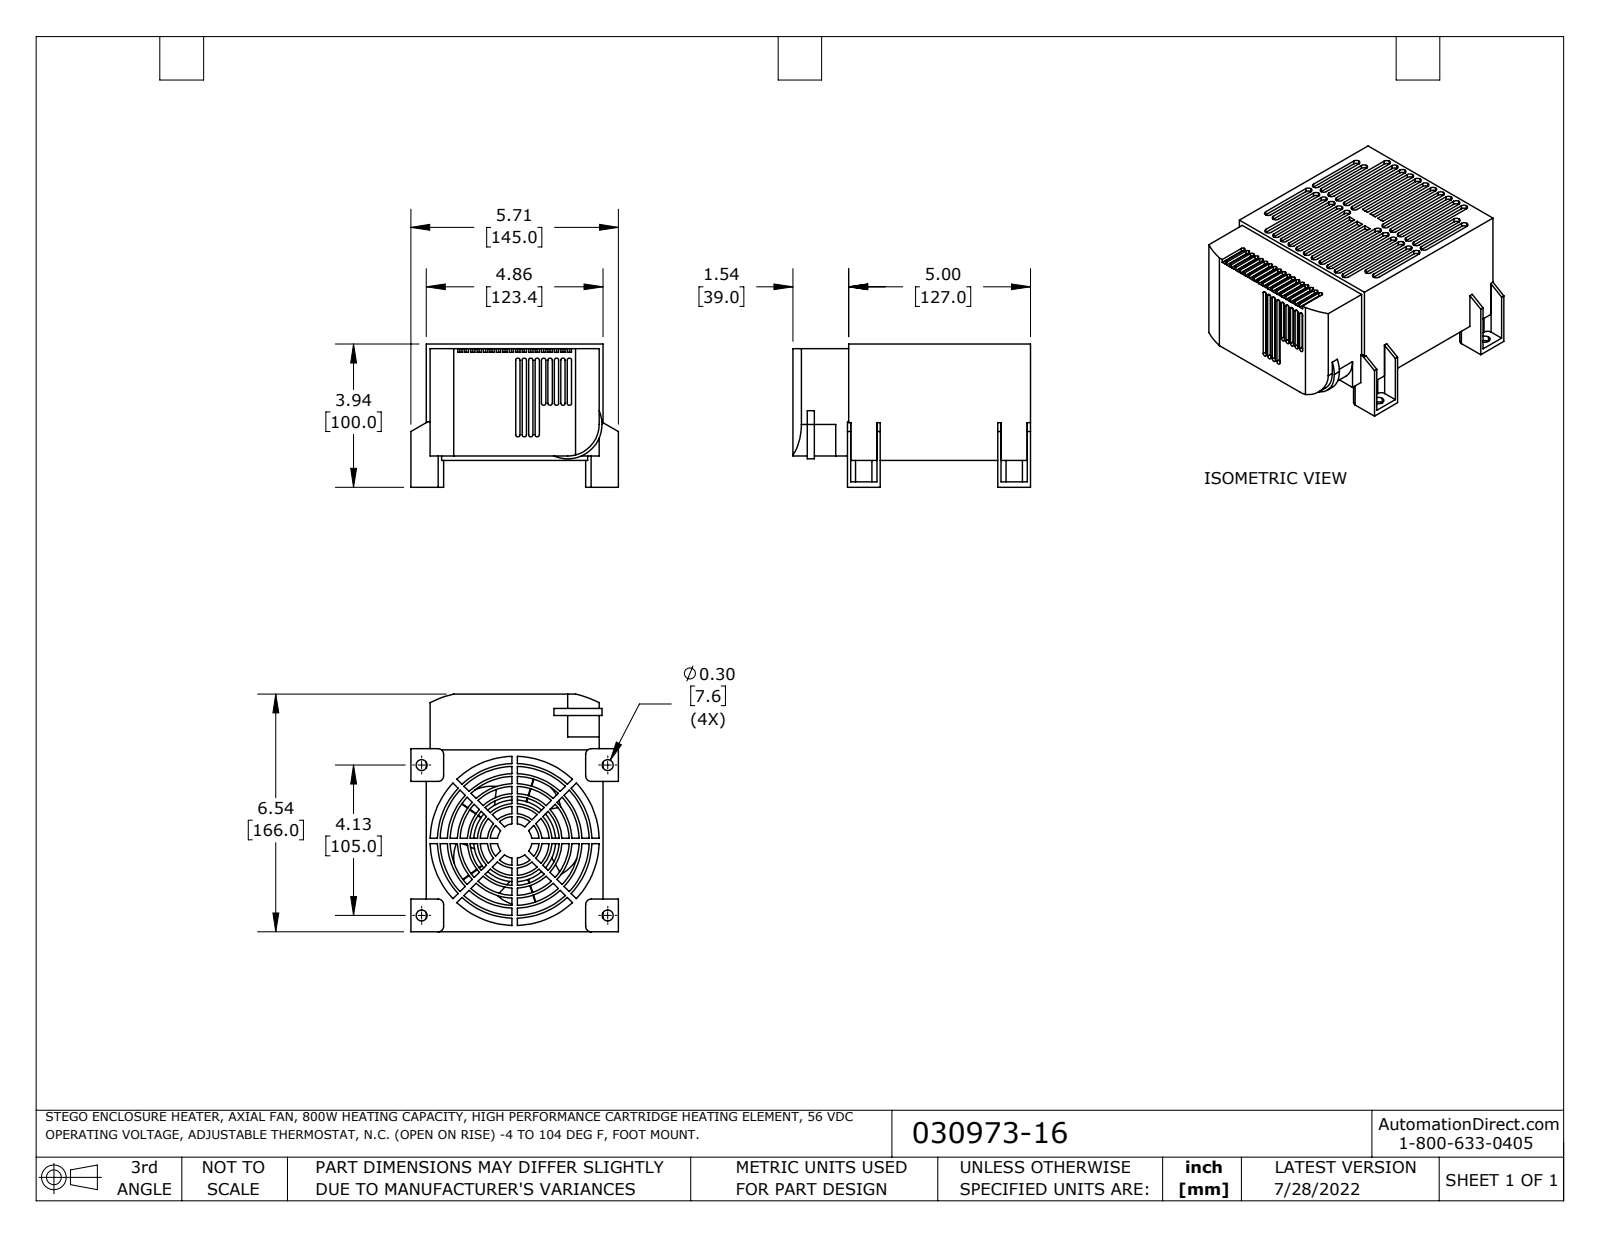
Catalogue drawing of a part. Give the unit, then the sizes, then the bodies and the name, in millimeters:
Units: millimetres
Overall size (bounding box): 166 × 145 × 100
Round holes (diameter × count): ⌀7.6 ×4, ⌀10 ×1, ⌀34.3 ×1, ⌀48.3 ×1, ⌀62.2 ×1, ⌀76.2 ×1, ⌀90.2 ×1, ⌀104.1 ×1, ⌀118.1 ×1
Round bosses / shafts (diameter × count): ⌀108 ×1, ⌀94 ×1, ⌀80 ×1, ⌀66 ×1, ⌀57.2 ×1, ⌀52.1 ×1, ⌀38.1 ×1, ⌀24.1 ×1
Partial cylindrical surfaces — rounded edges, fillets, slot ends (radius × count): R2.5 ×54, R1.5 ×36, R3.4 ×8, R3.8 ×8, R27.6 ×5, R70 ×2, R22 ×1, R24 ×1
Main face-to-face distances: 2.5, 123.4, 53.3, 3.1, 25.4, 78.7, 81.3, 55.9, 78.1, 10.2
Hole centre spacings: 83.3, 83.8, 105, 130, 167.1
Volume: 1 383 000 mm³ · Surface area: 154 600 mm²
Bodies: 1 solid, 667 faces (438 planar, 229 cylindrical, 0 other)
Part name (STEP PRODUCT): 030973-16_Default
STEP written by: SolidWorks 2021 (CONFIG_CONTROL_DESIGN)
